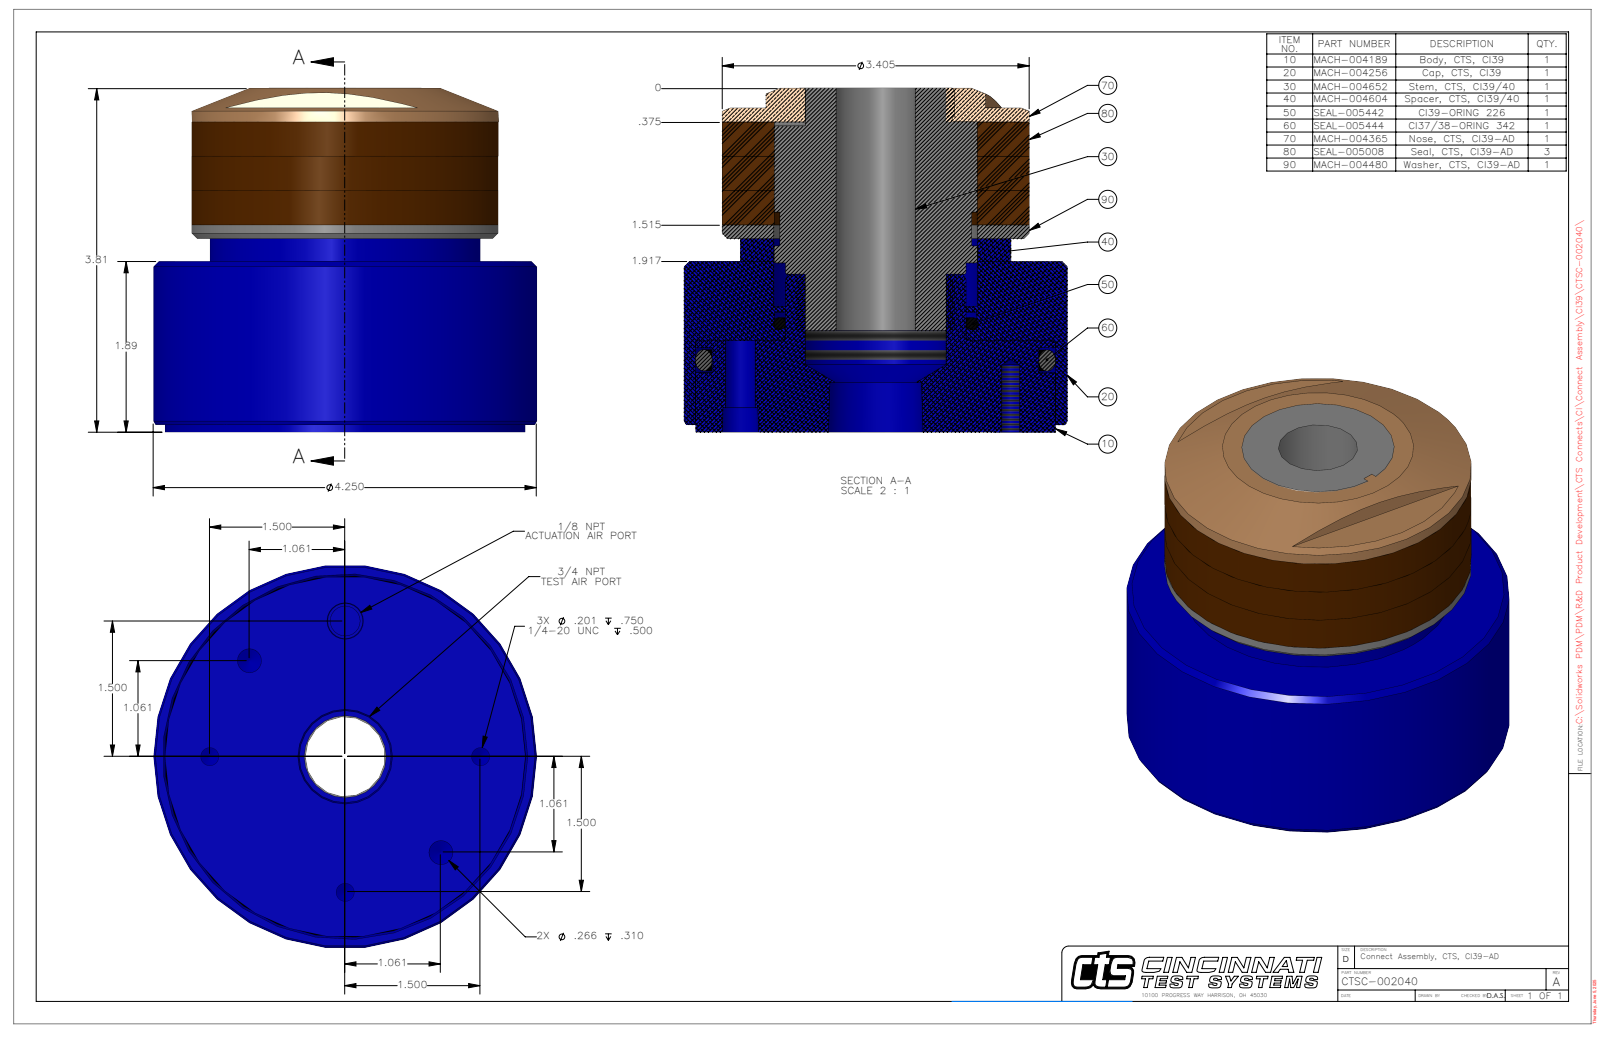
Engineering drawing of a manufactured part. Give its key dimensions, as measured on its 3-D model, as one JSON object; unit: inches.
{"part_name": "CTSC-002040", "step_written_by": "SolidWorks 2023 (AUTOMOTIVE_DESIGN)", "units": "inches", "bodies": {"solids": 1, "faces": 94, "planar": 32, "cylindrical": 39, "other": 23}, "overall_size": [4.25, 4.25, 3.813], "volume_in3": 40.1, "surface_area_in2": 105.8, "round_holes": [[0.201, 3], [0.266, 2], [0.332, 1], [0.88, 1], [2.25, 1], [2.26, 1], [2.261, 1], [4, 1]], "round_bosses_or_shafts": [[4.25, 1], [3.992, 1], [3.405, 1], [3, 1], [2.12, 1]], "partial_cylinders_radius": [[0.062, 1], [0.781, 1]], "face_to_face_distances": [1.893, 3.813, 1.92, 2.143, 0.25, 1.67, 3.81, 1.917, 1.667, 3.591], "hole_center_spacings": [1.5, 1.148, 2.121, 2.772, 3]}
